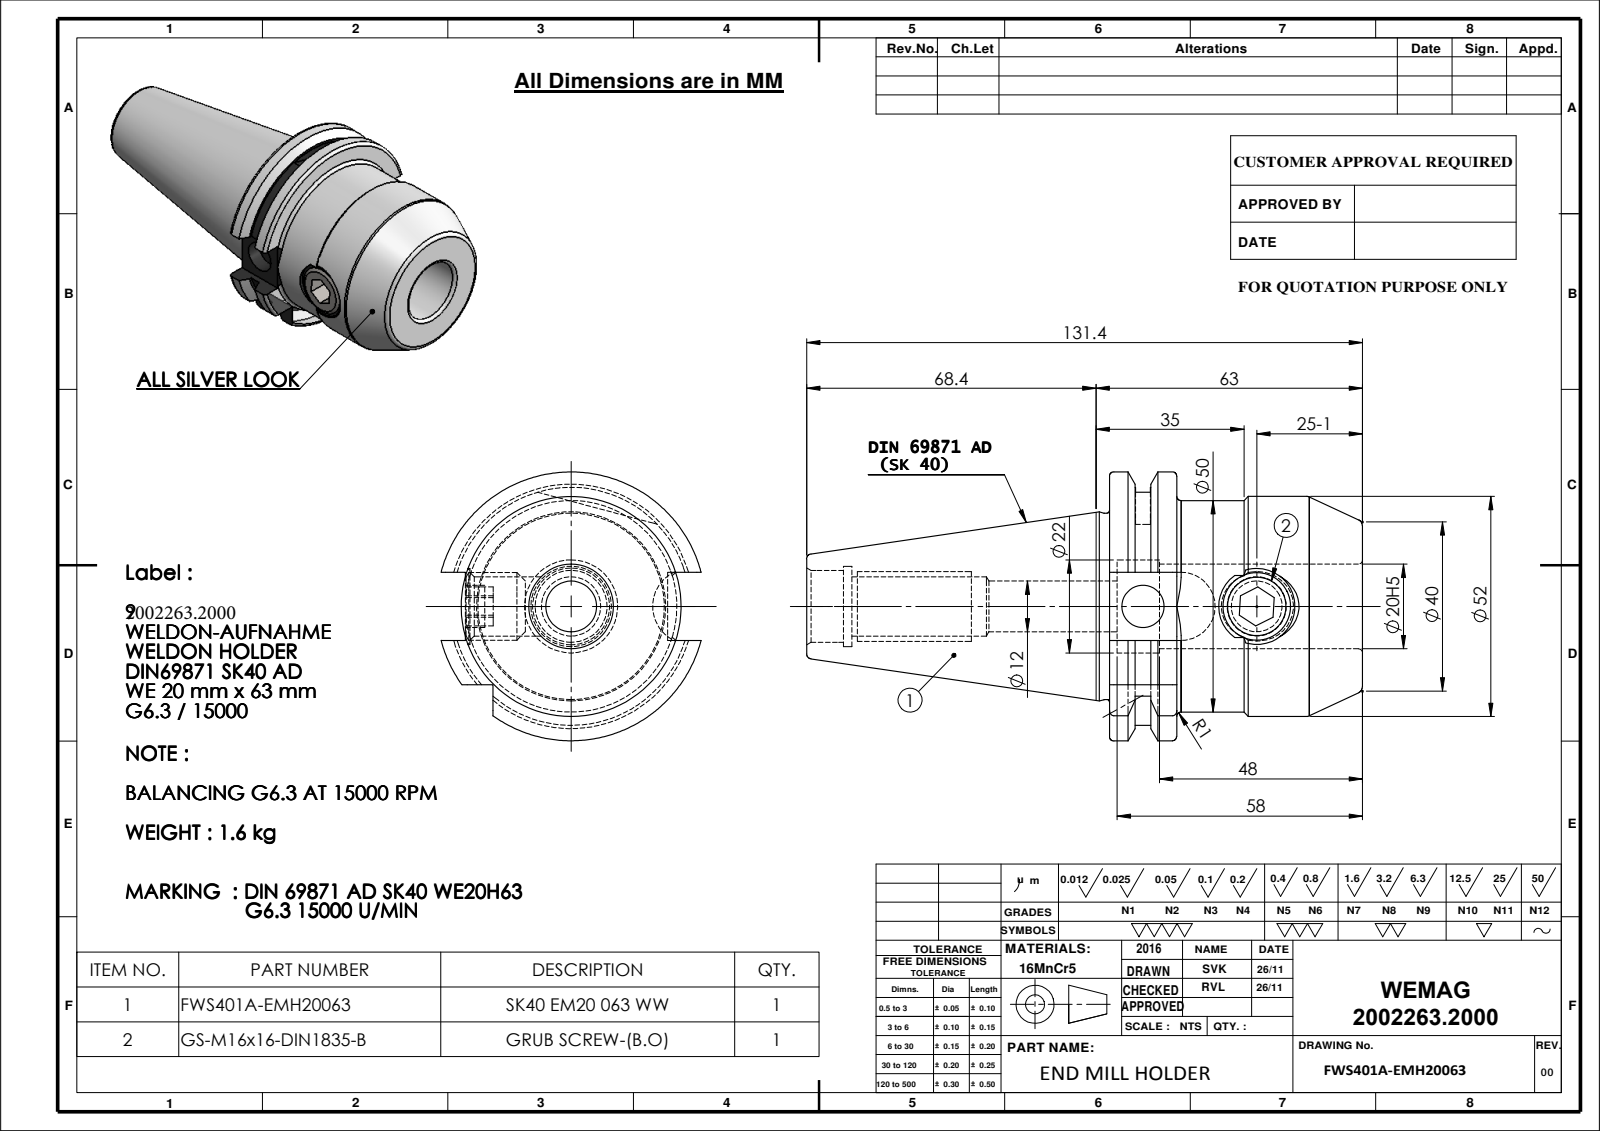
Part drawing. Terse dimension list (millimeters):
name: M16X16_ISO 4026 - M16 x 10-N; 91406-WE120063; SK40 EM 20 063 WW
written by: SolidWorks 2009 (CONFIG_CONTROL_DESIGN)
unit: mm
bodies: 2 solids, 134 faces (38 planar, 40 cylindrical, 56 other)
size: 131.4 × 63.55 × 61.48
volume: 166 829 mm³; area: 31 786 mm²
holes: 2× ⌀14, 1× ⌀10, 1× ⌀12, 1× ⌀17, 1× ⌀18, 1× ⌀19, 1× ⌀20, 1× ⌀22
bosses: 1× ⌀52, 1× ⌀50, 1× ⌀44.05, 1× ⌀16
rounds: 1× R8.05, 1× R28.12, 1× R31.77
face distances: 59.8, 15.9, 43.9, 1.8, 14.1, 58, 16.1, 47.8, 71.6, 73.4
hole spacings: 26.9
